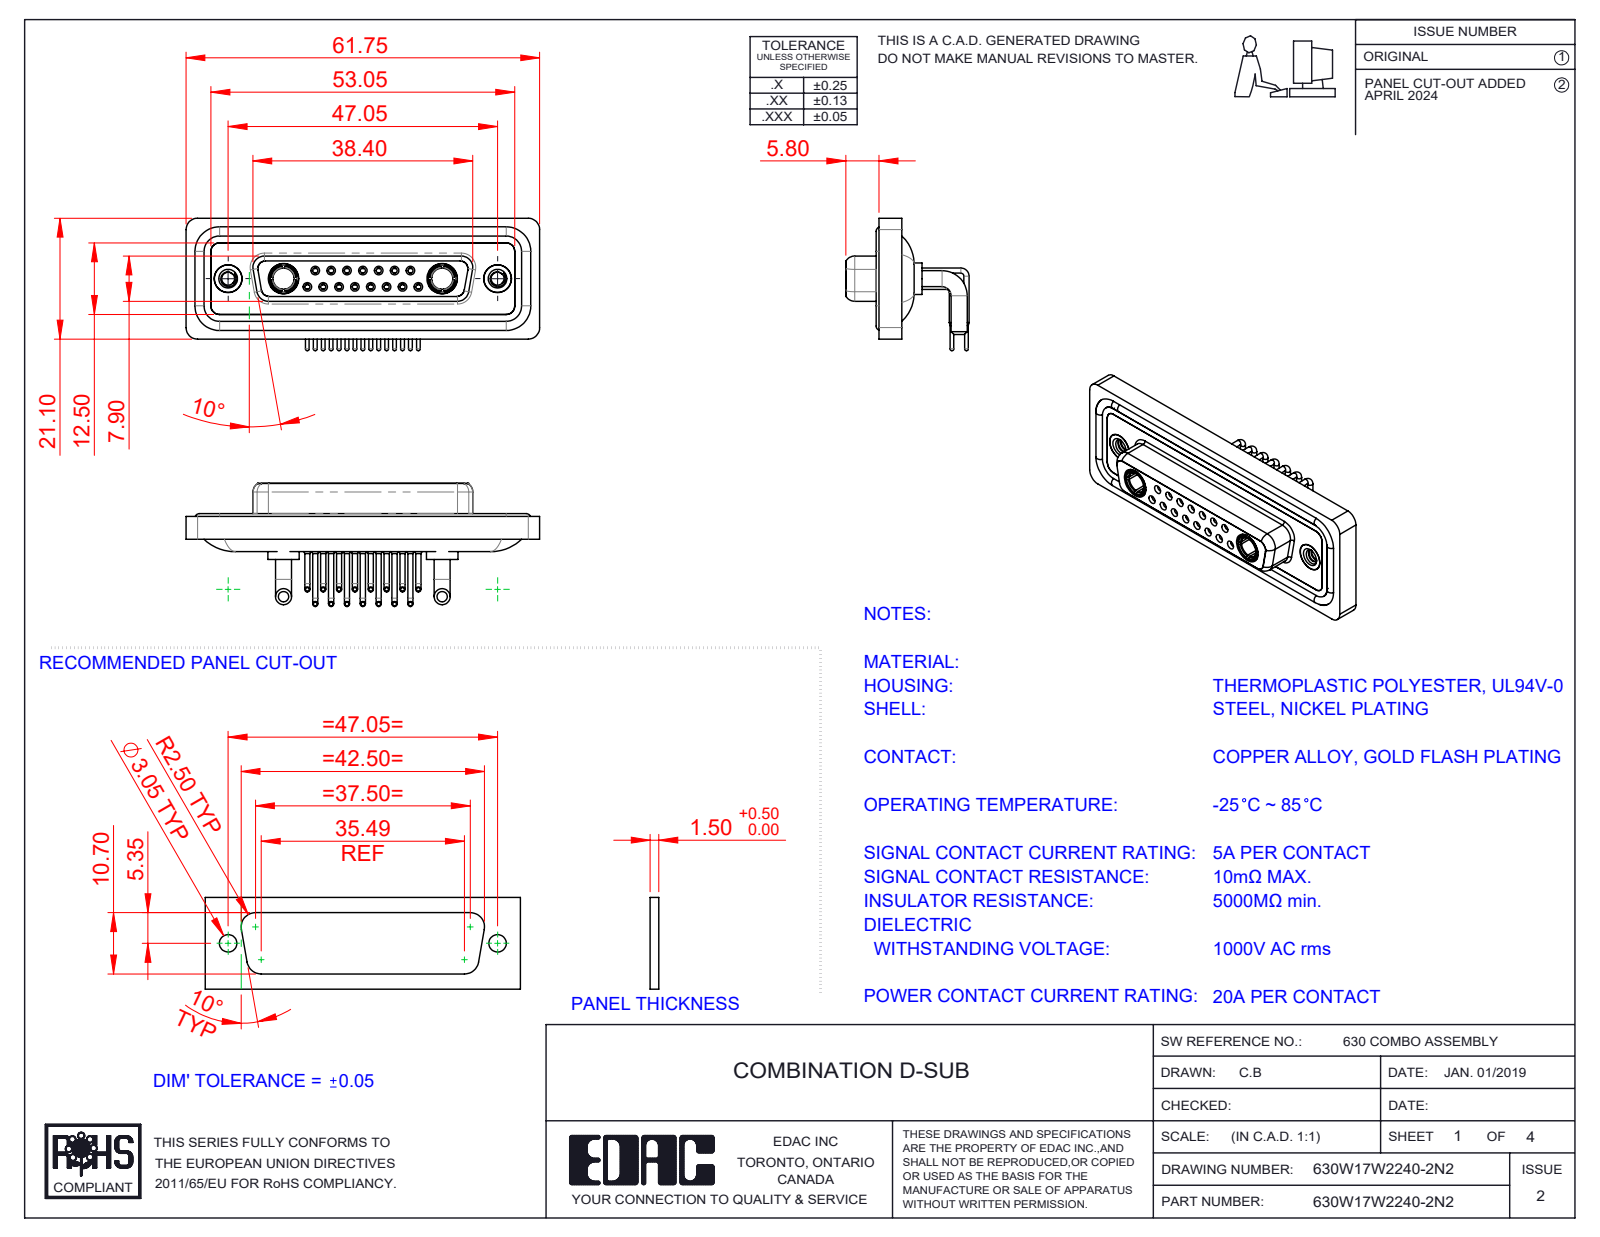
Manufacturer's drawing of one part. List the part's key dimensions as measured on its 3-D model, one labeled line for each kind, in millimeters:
Part name (STEP PRODUCT): 630Combo Shell Front_25 Contacts; 630Combo Shell Rear_25 Contacts; Power Socket_20A RA; 630W17W2140-2N2 (+5 more)
STEP written by: SolidWorks 2023 (CONFIG_CONTROL_DESIGN)
Units: millimetres
Bodies: 26 solids, 1337 faces (388 planar, 583 cylindrical, 366 other)
Overall size (bounding box): 61.75 × 23.12 × 21.53
Volume: 8 486 mm³ · Surface area: 14 530 mm²
Round holes (diameter × count): ⌀0.9 ×15, ⌀1.1 ×15, ⌀1.5 ×15, ⌀2 ×15, ⌀1.6 ×8, ⌀1.7 ×7, ⌀4.85 ×4, ⌀2.26 ×2, ⌀3.7 ×2, ⌀4 ×2, ⌀4.05 ×2, ⌀5 ×2
Round bosses / shafts (diameter × count): ⌀0.9 ×15, ⌀0.65 ×15, ⌀1.6 ×11, ⌀2.8 ×4, ⌀5.5 ×2, ⌀5.2 ×2, ⌀4.96 ×2, ⌀4.95 ×2
Partial cylindrical surfaces — rounded edges, fillets, slot ends (radius × count): R1.5 ×18, R2 ×18, R1.35 ×8, R1.6 ×8, R0.25 ×4, R0.5 ×4, R0.6 ×4, R0.65 ×4
Main face-to-face distances: 0.4, 1.8, 4.1, 1.1, 1.6, 3.1, 2.5, 1.5, 3.7, 1.4
Hole centre spacings: 3.16, 2.77, 5.54, 8.31, 5.04, 7.49, 11.08, 5.03
